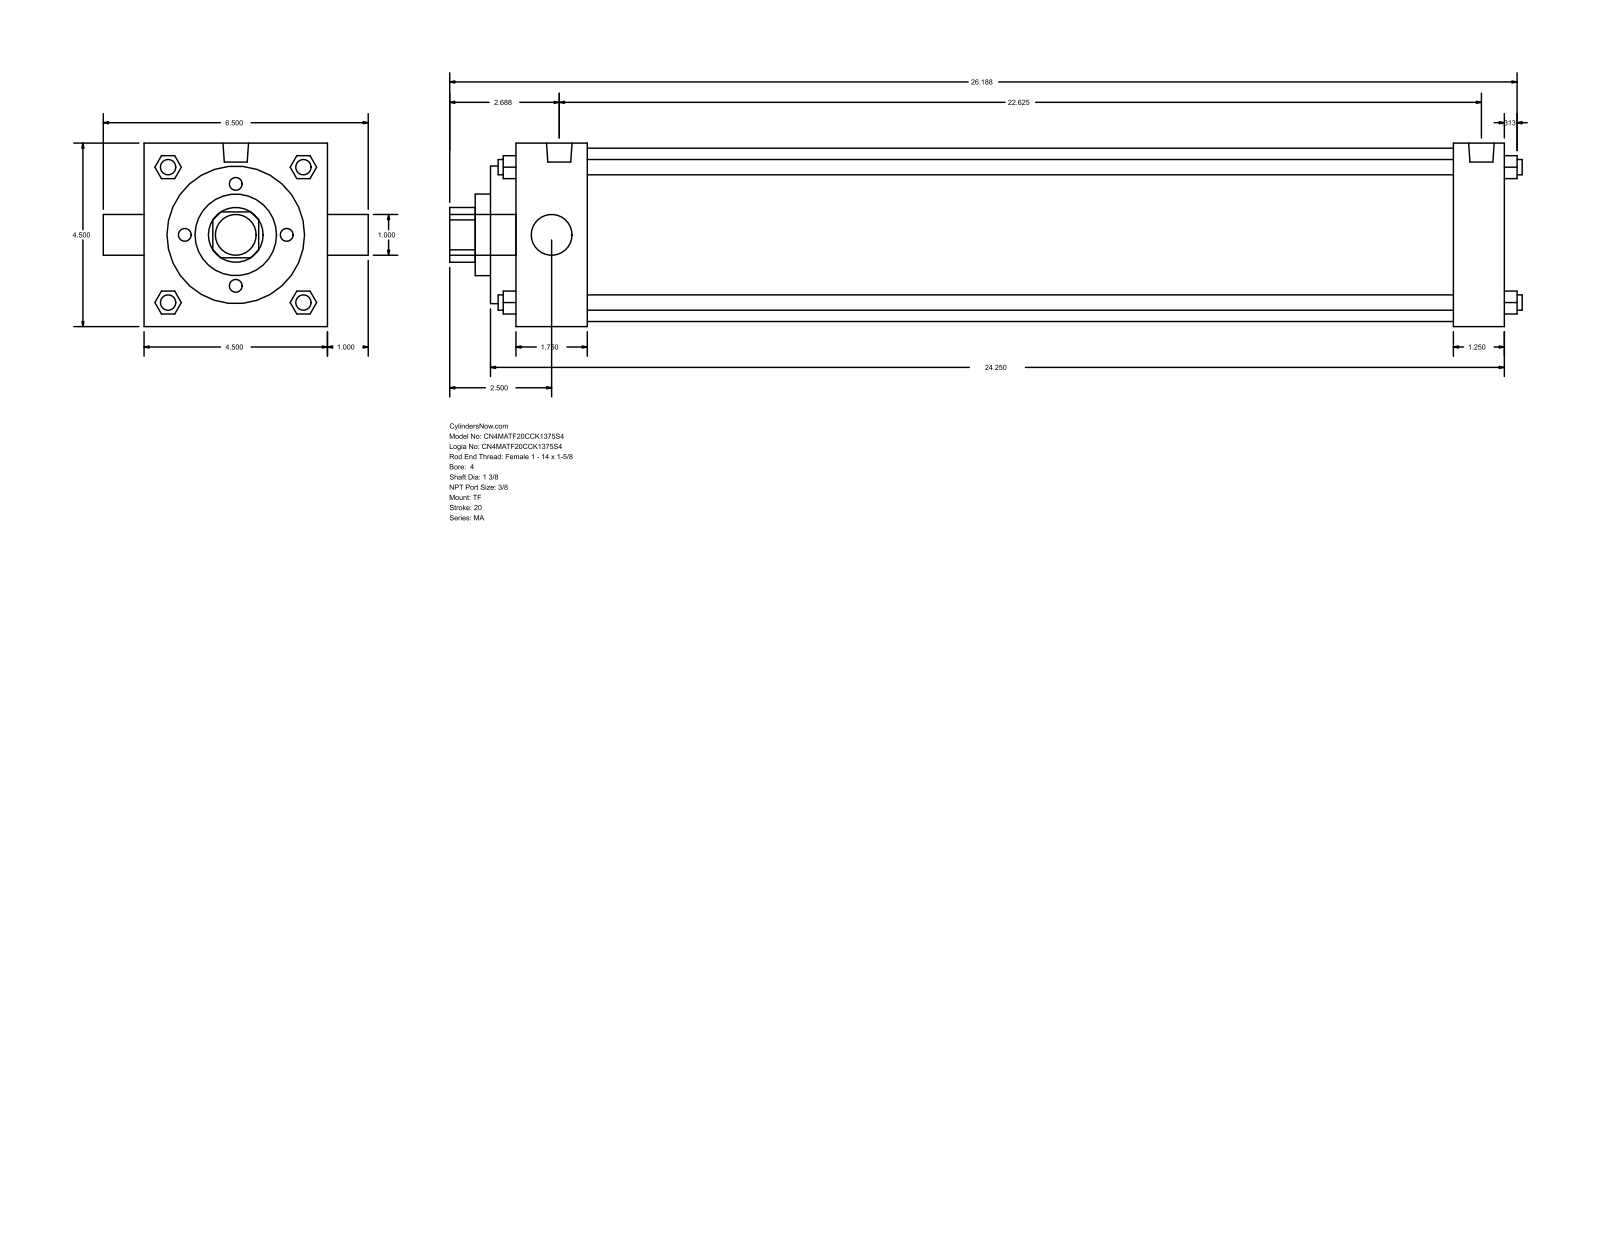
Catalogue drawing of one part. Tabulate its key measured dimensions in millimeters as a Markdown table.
| quantity | value |
| --- | --- |
| part name | MA_TF__0400_1.375 |
| STEP written by | GSSL Pune (CONFIG_CONTROL_DESIGN) |
| units | millimeters |
| bodies | 0 solids, 122 faces (93 planar, 29 cylindrical, 0 other) |
| overall size | 668.34 × 165.1 × 114.3 |
| round holes (diameter × count) | 25.4 × 1, 34.92 × 1, 50.8 × 1, 85.72 × 1, 107.95 × 1 |
| round bosses / shafts (diameter × count) | 9.53 × 4, 11.11 × 3, 15.93 × 2, 25.4 × 1 |
| partial cylindrical surfaces (radius × count) | 17.06 × 1 |
| main face-to-face distances | 114.3, 615.96, 15.87, 631.83, 600.08, 584.21, 31.75, 60.32, 44.45, 539.76 |
